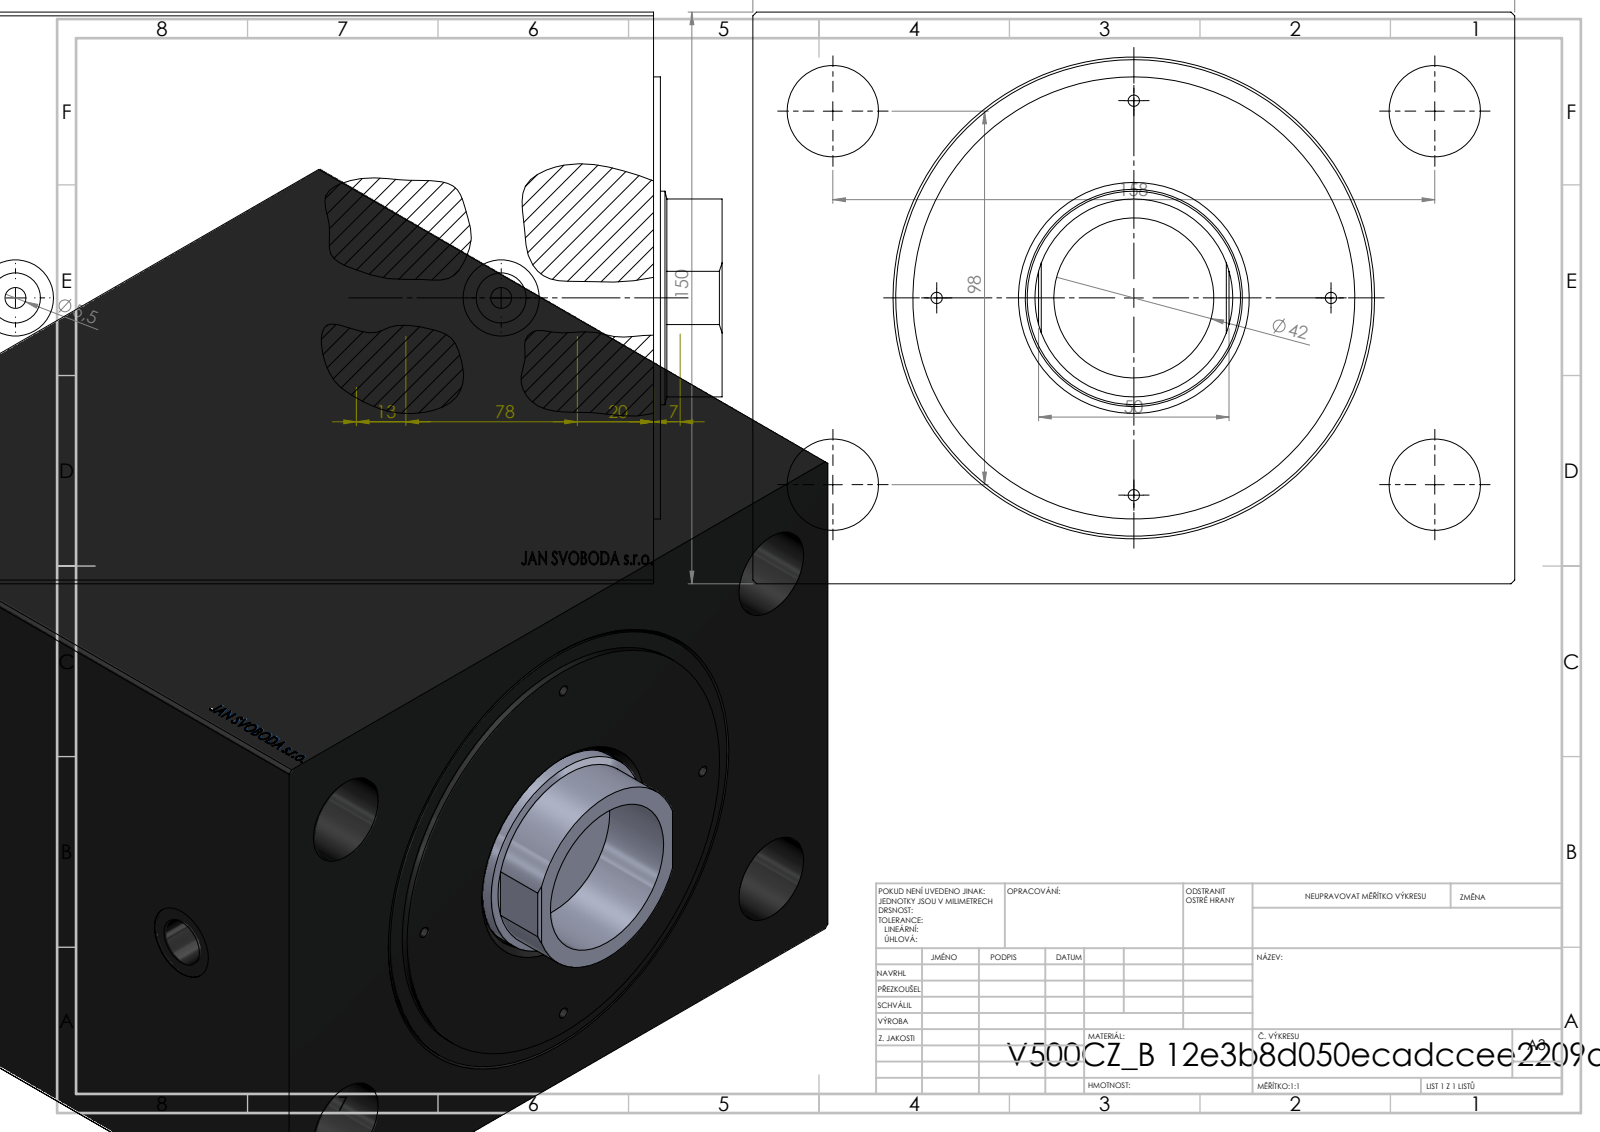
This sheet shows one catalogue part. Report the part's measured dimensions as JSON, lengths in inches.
{"part_name": "V500CZ_vnitrni_cast_vysunovaci; V500CZ", "step_written_by": "SolidWorks 2019 (CONFIG_CONTROL_DESIGN)", "units": "inches", "bodies": {"solids": 3, "faces": 888, "planar": 407, "cylindrical": 71, "other": 410}, "overall_size": [8.11, 7.874, 5.906], "volume_in3": 323.2, "surface_area_in2": 467.5, "round_holes": [[0.118, 4], [0.945, 4], [0.217, 2], [0.518, 2], [0.787, 2], [1.417, 1], [1.654, 1], [2.205, 1], [2.244, 1], [3.937, 1], [4.921, 1]], "round_bosses_or_shafts": [[4.567, 1], [2.044, 1]], "face_to_face_distances": [5.906, 7.874, 7.402, 4.055, 3.346, 2.953, 0.394, 7.008, 0.071, 0.465], "hole_center_spacings": [2.037, 2.207, 2.881, 3.112, 3.66, 5.041, 5.497, 3.858]}
